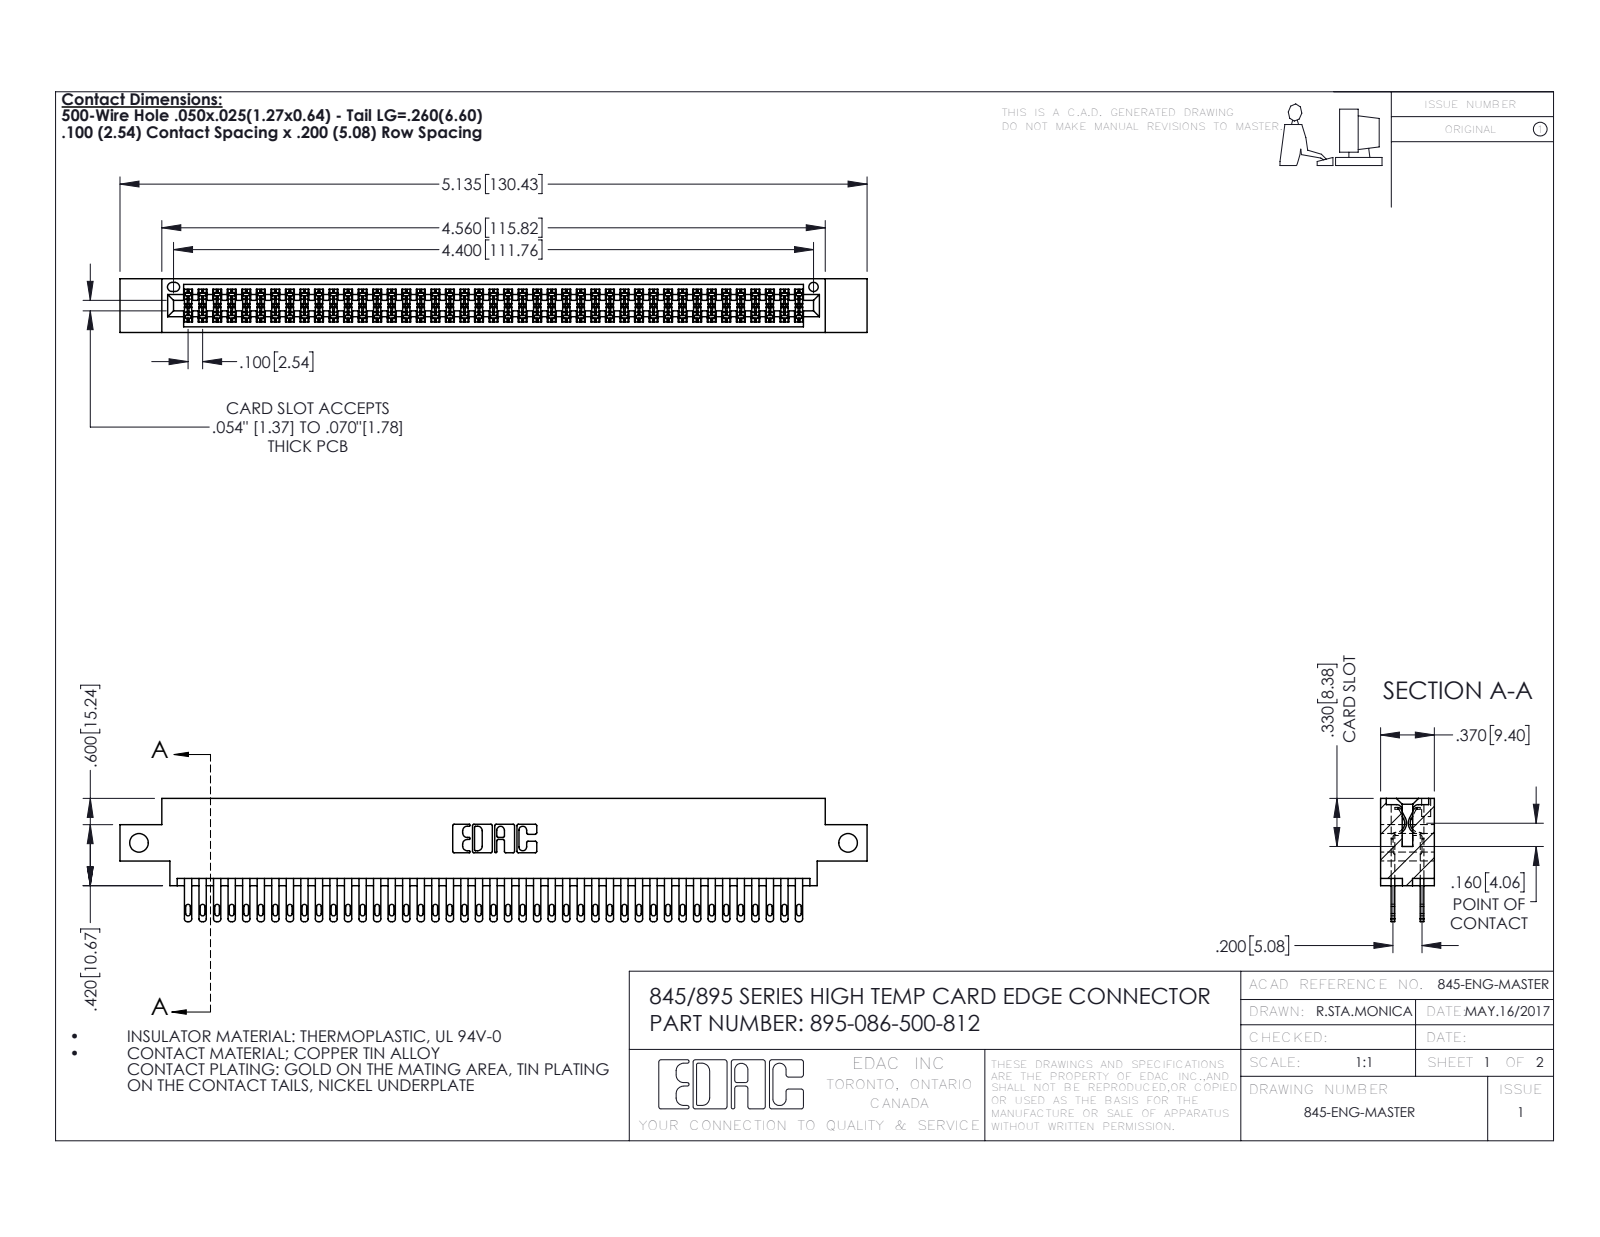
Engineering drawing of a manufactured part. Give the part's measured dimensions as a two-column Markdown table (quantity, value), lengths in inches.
| quantity | value |
| --- | --- |
| part name | 345 Part_0.170 Offset - Side Mount; 345-292-001_345-293-100; 345-086-500-812 |
| STEP written by | SolidWorks 2016 (CONFIG_CONTROL_DESIGN) |
| units | inches |
| bodies | 87 solids, 4086 faces (2406 planar, 1680 cylindrical, 0 other) |
| overall size | 5.135 × 0.847 × 0.37 |
| volume | 0.778 in³ |
| surface area | 30.59 in² |
| round holes (diameter × count) | 0.128 × 2, 0.064 × 1 |
| partial cylindrical surfaces (radius × count) | 0.006 × 129, 0.016 × 86, 0.02 × 86, 0.01 × 22, 0.007 × 6, 0.031 × 6, 0.026 × 3, 0.014 × 2 |
| main face-to-face distances | 0.298, 0.072, 0.2, 0.098, 0.272, 0.025, 0.37, 0.225, 0.175, 0.149 |
| hole center spacings | 4.875 |
